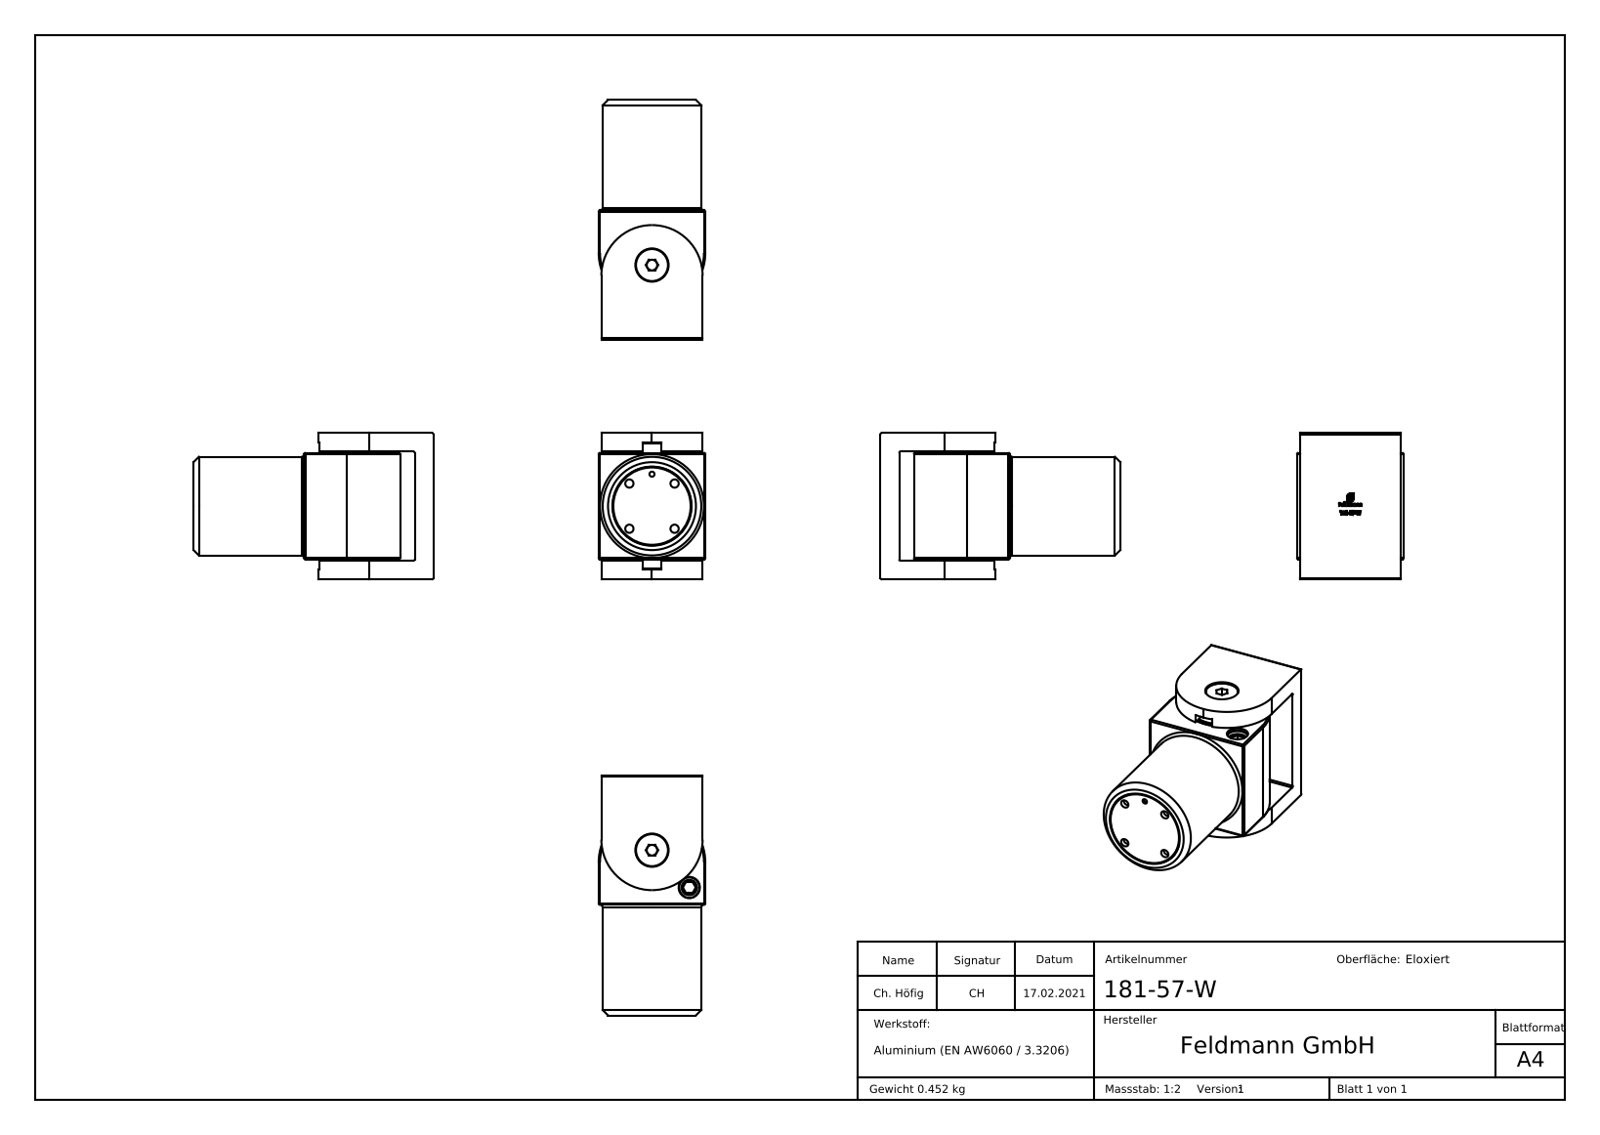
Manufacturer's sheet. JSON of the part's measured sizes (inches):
{"part_name": "Teil1_181-57-W Teil1; DIN-7991 M3-M10; Teil1; 181-57-W (+3 more)", "step_written_by": "SolidWorks 2018 (CONFIG_CONTROL_DESIGN)", "units": "inches", "bodies": {"solids": 5, "faces": 470, "planar": 233, "cylindrical": 80, "other": 157}, "overall_size": [551.199, 236.22, 236.22], "volume_in3": 7.674, "surface_area_in2": 41.38, "round_holes": [[0.122, 4], [0.075, 1], [0.197, 1], [0.256, 1], [0.315, 1], [0.492, 1], [0.618, 1], [0.945, 1], [1.169, 1]], "round_bosses_or_shafts": [[1.457, 1], [1.161, 1], [1.024, 1], [0.929, 1], [0.61, 1], [0.472, 1], [0.307, 1], [0.236, 1]], "partial_cylinders_radius": [[0.02, 12], [0.748, 1], [0.787, 1]], "face_to_face_distances": [0.276, 1.89, 1.87, 0.02, 0.295, 1.594, 2.165, 1.575, 0.039, 1.535], "hole_center_spacings": [0.473, 0.669, 0.362, 0.873, 0.945, 0.472, 0.78]}
